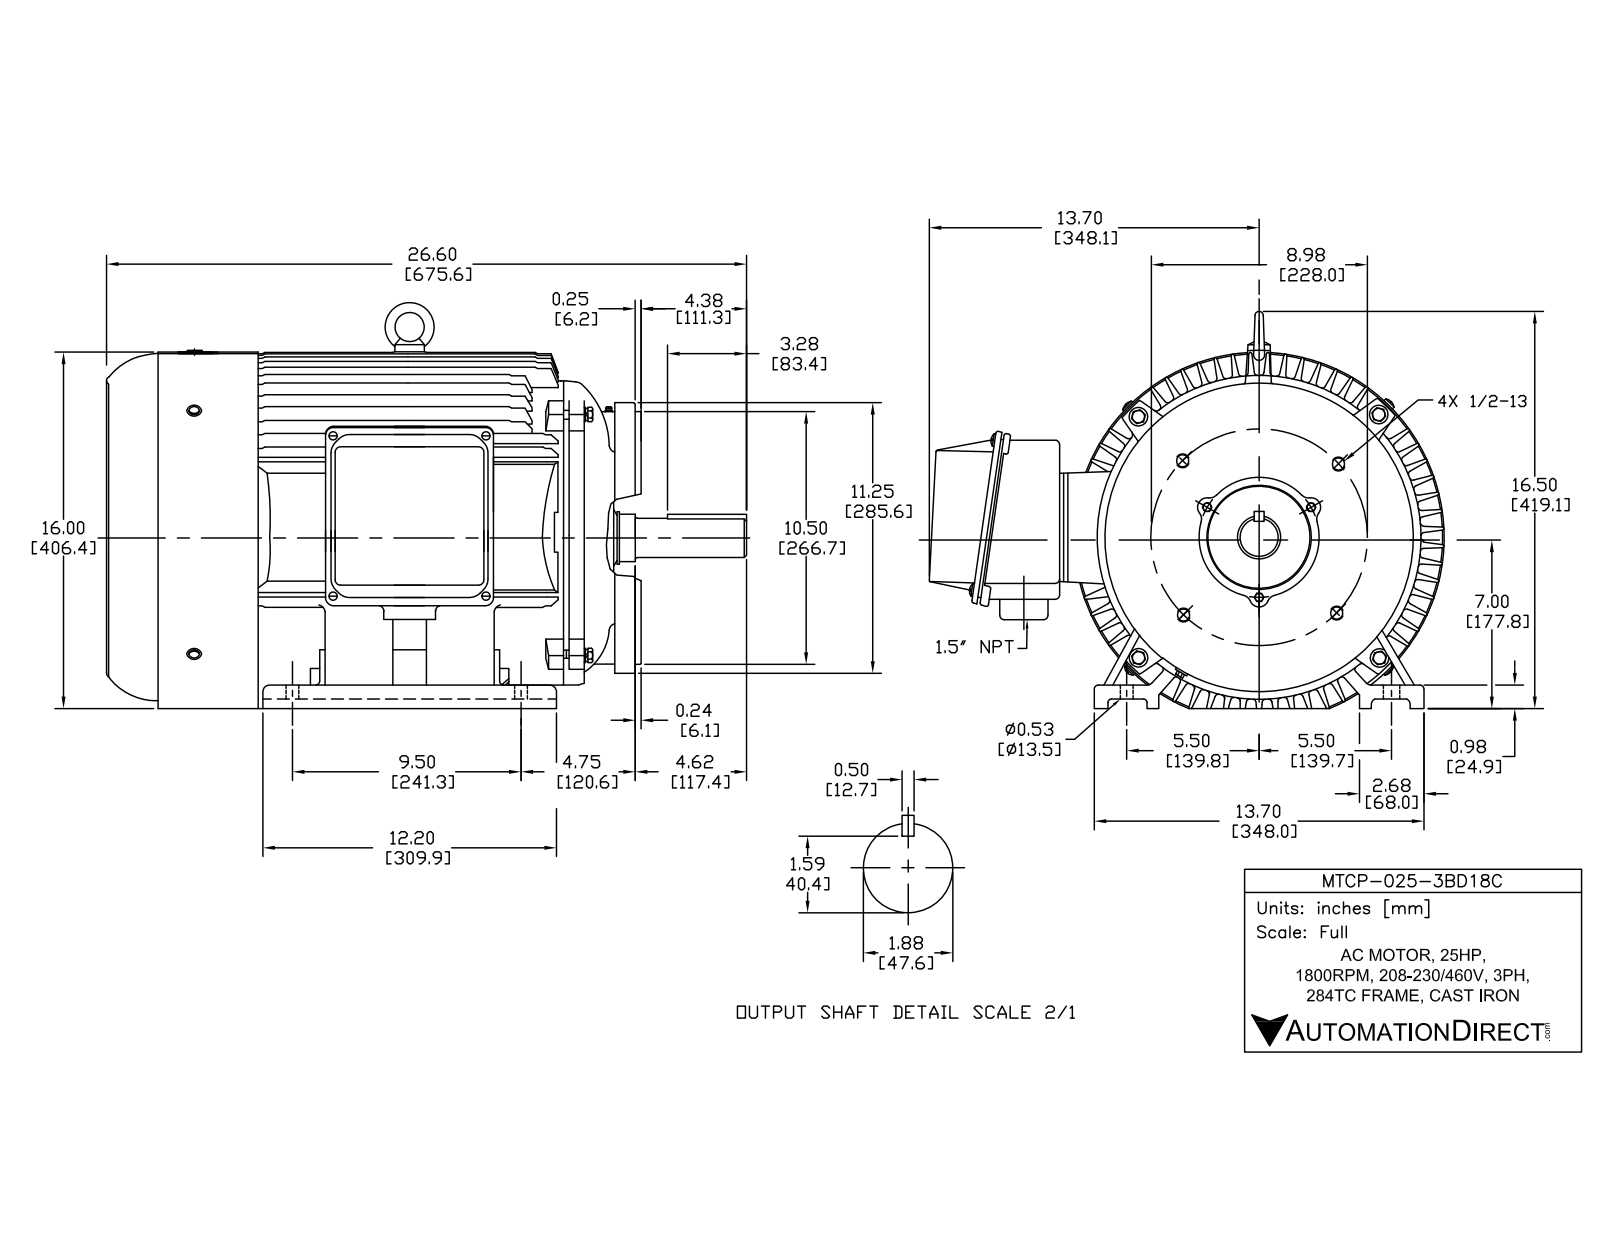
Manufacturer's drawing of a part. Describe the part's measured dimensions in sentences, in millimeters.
The part is named "PE280前轴承外盖加工件; plain washers-chamfered--normal series-a gb_GB_FASTENER_WASHER_SWCA 6; hexagon head bolts-full thread gb_GB_FASTENER_BOLT_STBAB A M8X50-N; MTCP-025-3BD18C (+8 more)". Its 3-D file was written by "SolidWorks 2017 (AUTOMOTIVE_DESIGN)". It is 68 solids with 4086 faces: 1064 planar, 1435 cylindrical and 1587 other. Overall it measures 679.5 by 489.93 by 443 millimeters. Its volume is 11 900 000 cubic millimeters and its surface area 3 098 000 square millimeters. Round holes: 14 of diameter 7, 10 of diameter 10, 8 of diameter 5, 4 of diameter 6.4, 4 of diameter 6.68, 4 of diameter 6.8, 4 of diameter 9, 4 of diameter 10.2, 4 of diameter 10.72, 4 of diameter 11.39, 4 of diameter 12.9, 4 of diameter 13. Round bosses or shafts: 8 of diameter 12, 8 of diameter 6, 6 of diameter 8, 4 of diameter 24, 4 of diameter 19.1, 4 of diameter 9.88, 4 of diameter 5, 2 of diameter 10. Partial cylindrical surfaces (rounded edges, fillets, slot ends): 265 of radius 1, 76 of radius 3, 74 of radius 5, 48 of radius 0.5, 46 of radius 2, 36 of radius 1.5, 26 of radius 8, 24 of radius 0.75. The main face-to-face distances are 1.5, 5, 12, 543.8, 542.3, 6.5, 10, 349, 561.8, 560.3. The hole center spacings are 144, 100, 216.18, 65, 70, 116.94, 213.78, 67.64.
